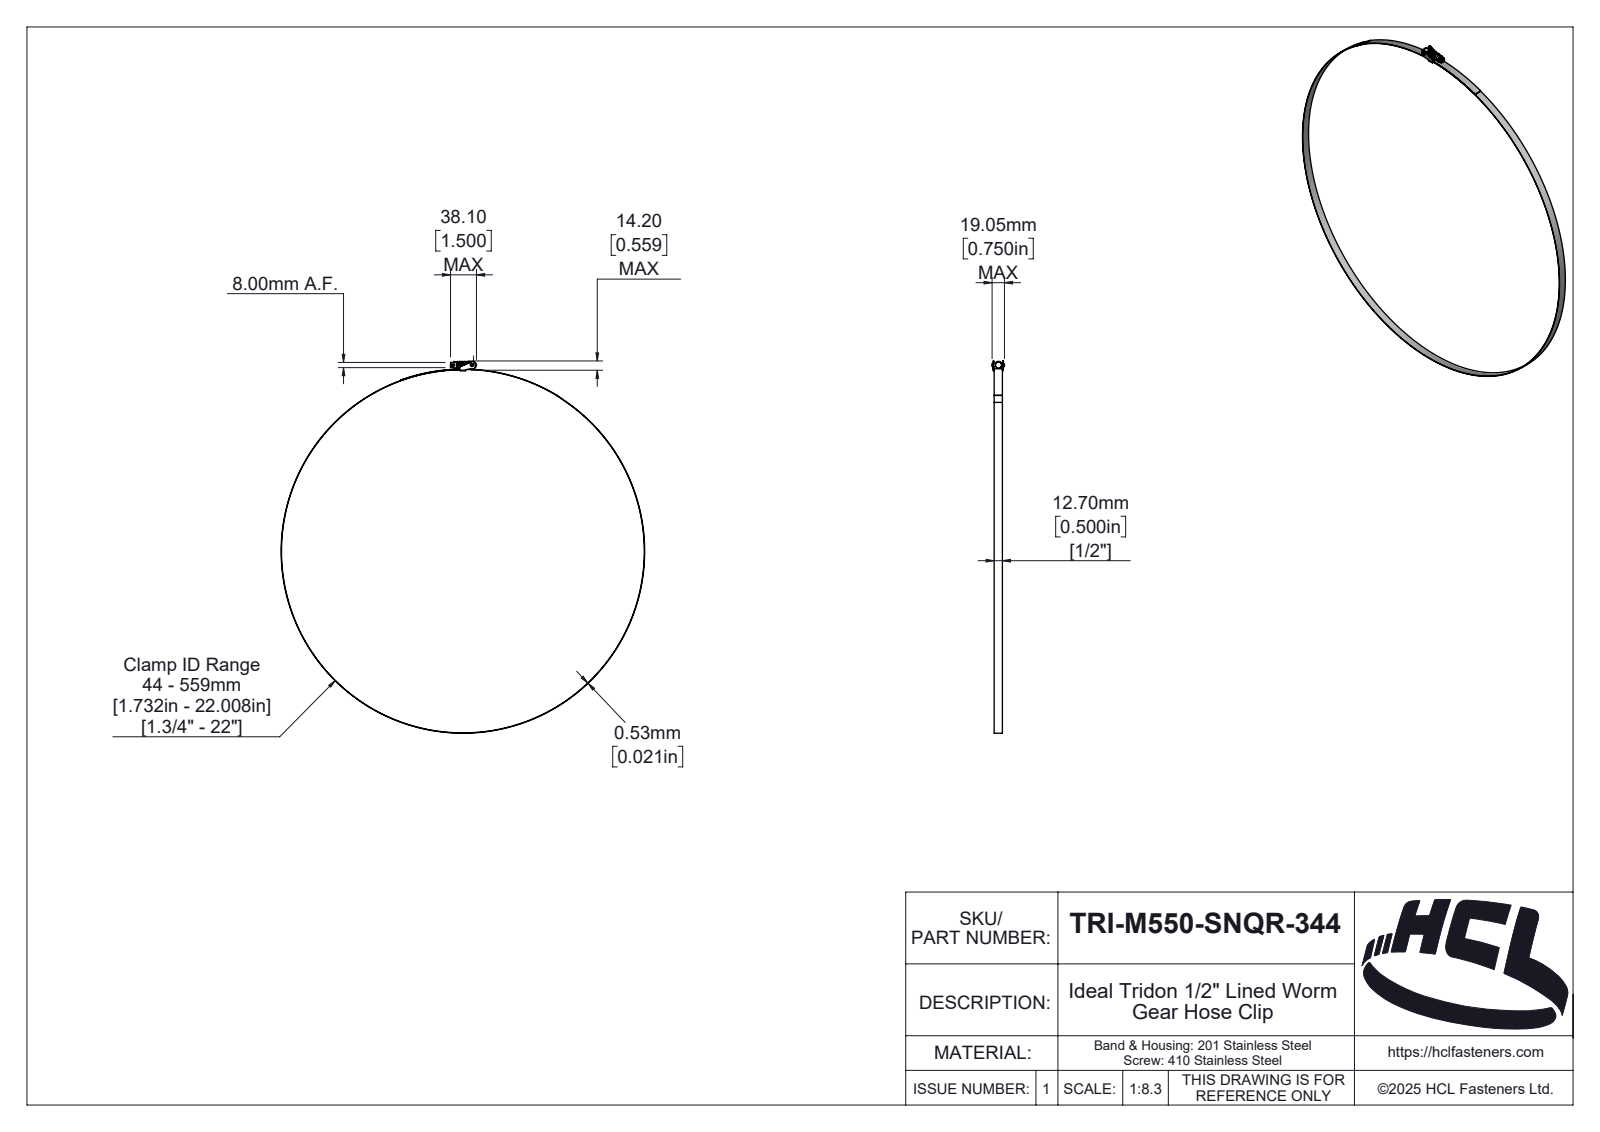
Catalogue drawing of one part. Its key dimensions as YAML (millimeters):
part_name: "TRI-M550-SNQR-344"
step_written_by: "SolidWorks 2025 (AUTOMOTIVE_DESIGN)"
units: millimeters
bodies: {solids: 5, faces: 222, planar: 44, cylindrical: 112, other: 66}
overall_size: [573.02, 560.06, 19.05]
volume: 15671
surface_area: 52693
round_holes:
  - {diameter: 5, count: 1}
  - {diameter: 559, count: 1}
round_bosses_or_shafts:
  - {diameter: 560.06, count: 1}
  - {diameter: 9.1, count: 1}
partial_cylinders:
  - {radius: 1, count: 11}
  - {radius: 0.1, count: 2}
  - {radius: 0.9, count: 2}
  - {radius: 3, count: 2}
  - {radius: 0.46, count: 1}
  - {radius: 1.89, count: 1}
  - {radius: 2, count: 1}
  - {radius: 2.35, count: 1}
face_to_face_distances: [12.7, 0.8, 1.35, 14.05, 14.6, 0.55, 13.25, 0.53, 15.4, 13.8]
hole_center_spacings: [287.24]
